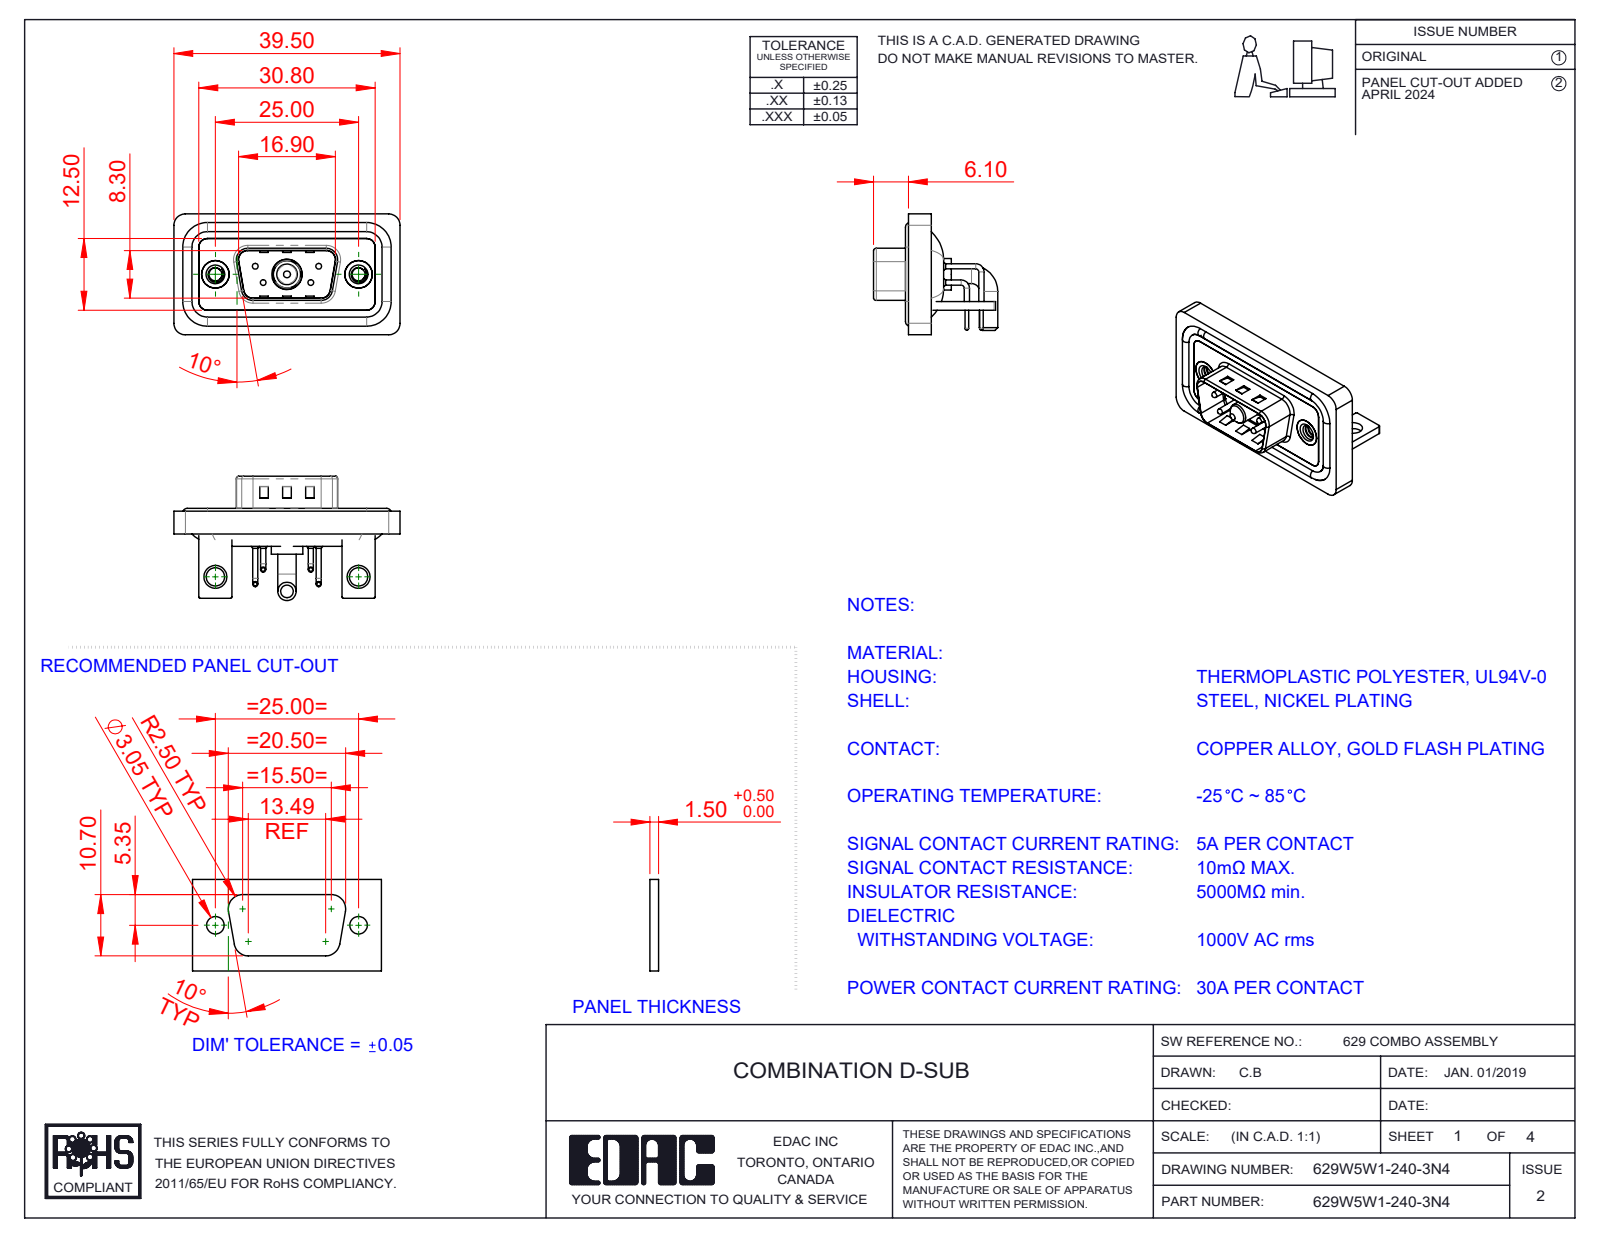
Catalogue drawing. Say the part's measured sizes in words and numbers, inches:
The part is named "629Combo Contact Row 1; 629Combo Shell Rear_09 Contacts; 629Combo Shell Front_09 Contacts; 629Combo Waterproof Housing_09 Contacts (+6 more)". Its 3-D file was written by "SolidWorks 2023 (CONFIG_CONTROL_DESIGN)". It is 15 solids with 934 faces: 431 planar, 363 cylindrical and 140 other. Overall it measures 1.555 by 0.854 by 0.831 inches. Its volume is 0.292 cubic inches and its surface area 12.04 square inches. Round holes: 4 of diameter 0.03, 4 of diameter 0.063, 4 of diameter 0.079, 2 of diameter 0.089, 2 of diameter 0.126, 2 of diameter 0.157, 2 of diameter 0.189, 2 of diameter 0.197, 1 of diameter 0.191, 1 of diameter 0.209. Round bosses or shafts: 8 of diameter 0.035, 4 of diameter 0.063, 4 of diameter 0.059, 4 of diameter 0.039, 4 of diameter 0.026, 2 of diameter 0.193, 2 of diameter 0.126, 1 of diameter 0.217. Partial cylindrical surfaces (rounded edges, fillets, slot ends): 19 of radius 0.079, 18 of radius 0.059, 16 of radius 0.01, 9 of radius 0.02, 8 of radius 0.063, 4 of radius 0.024, 4 of radius 0.026, 4 of radius 0.035. The main face-to-face distances are 0.016, 0.059, 0.031, 0.114, 0.043, 0.083, 0.047, 0.063, 0.098, 0.146. The hole center spacings are 0.124, 0.225, 0.28, 0.492, 0.713, 0.984, 0.173, 0.173.
